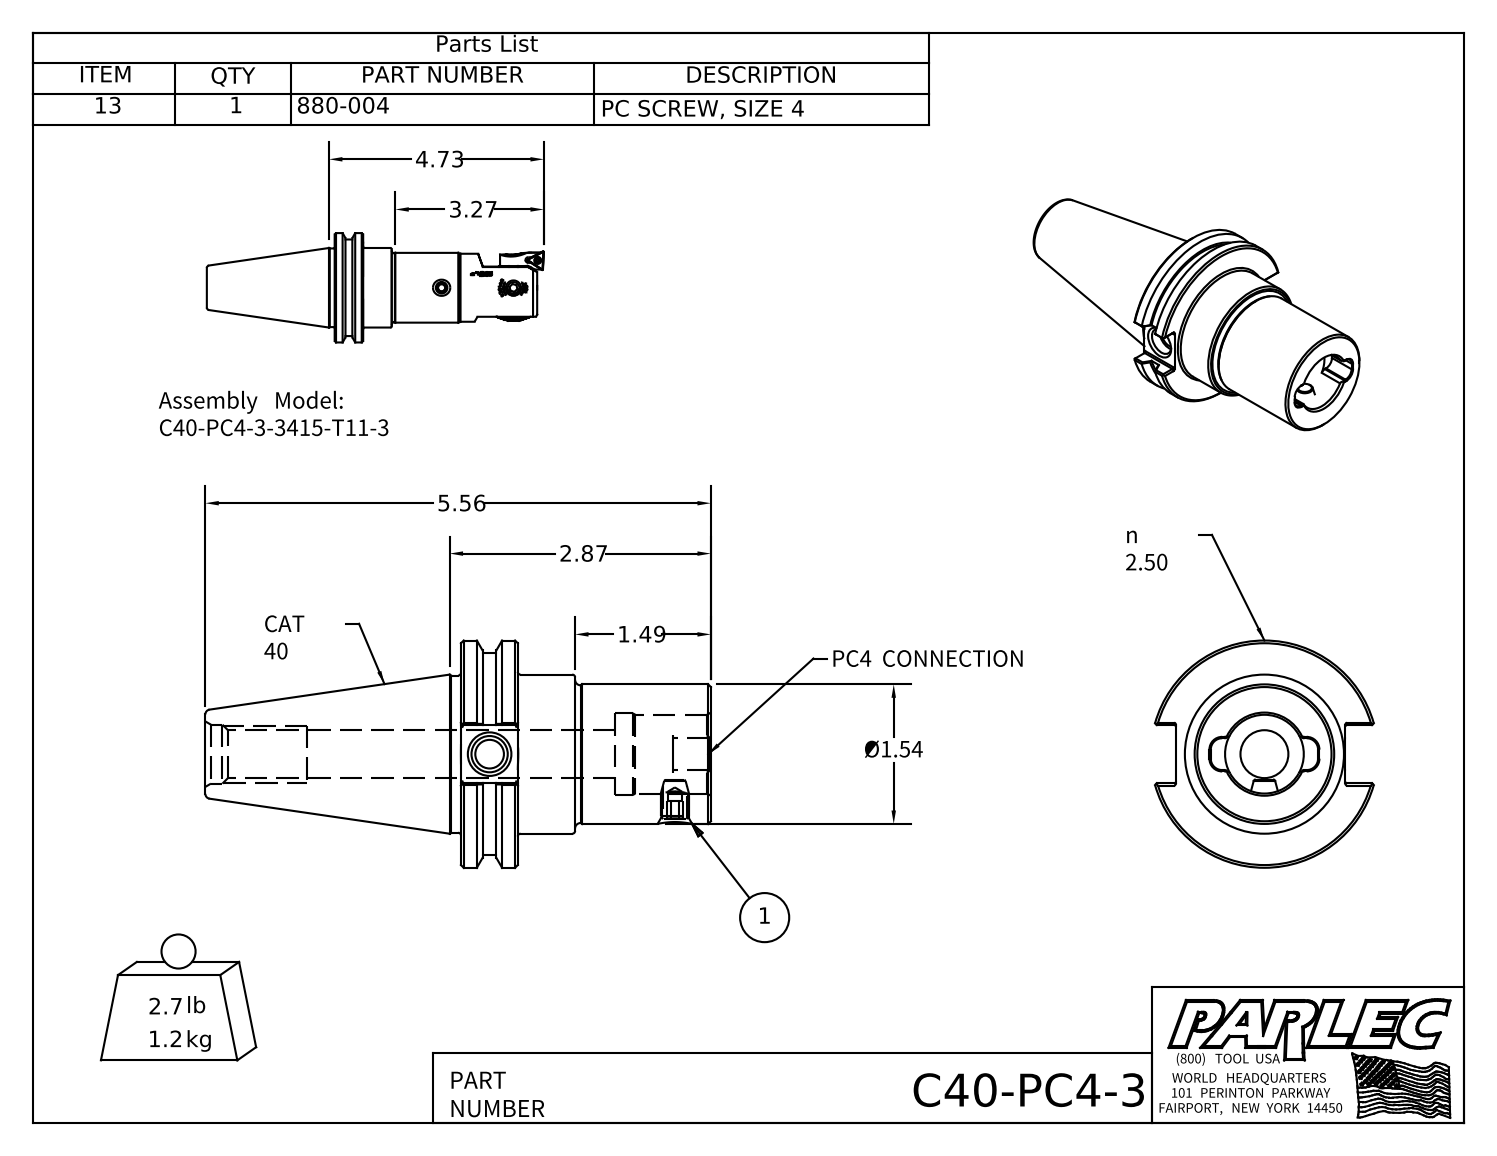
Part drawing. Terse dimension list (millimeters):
name: C40-PC4-3; C40-PC4-3-1; 880-004
written by: Autodesk Inventor 2018 (AUTOMOTIVE_DESIGN)
unit: mm
bodies: 2 solids, 146 faces (61 planar, 39 cylindrical, 46 other)
size: 141.2 × 63.5 × 61.1
volume: 155 600 mm³; area: 30 560 mm²
holes: 1× ⌀4, 1× ⌀7.2, 1× ⌀8, 1× ⌀10.1, 1× ⌀13.4, 1× ⌀16.5, 1× ⌀22, 1× ⌀22.9
bosses: 1× ⌀63.5, 1× ⌀56.4, 1× ⌀44.5, 1× ⌀43.9, 1× ⌀39, 1× ⌀38.5, 1× ⌀8
rounds: 12× R0.5, 4× R1.8, 4× R3.2
face distances: 15.9, 69.8, 53.9, 26.7, 43.1, 27.3, 16.3, 47.2, 71.4, 87.3
